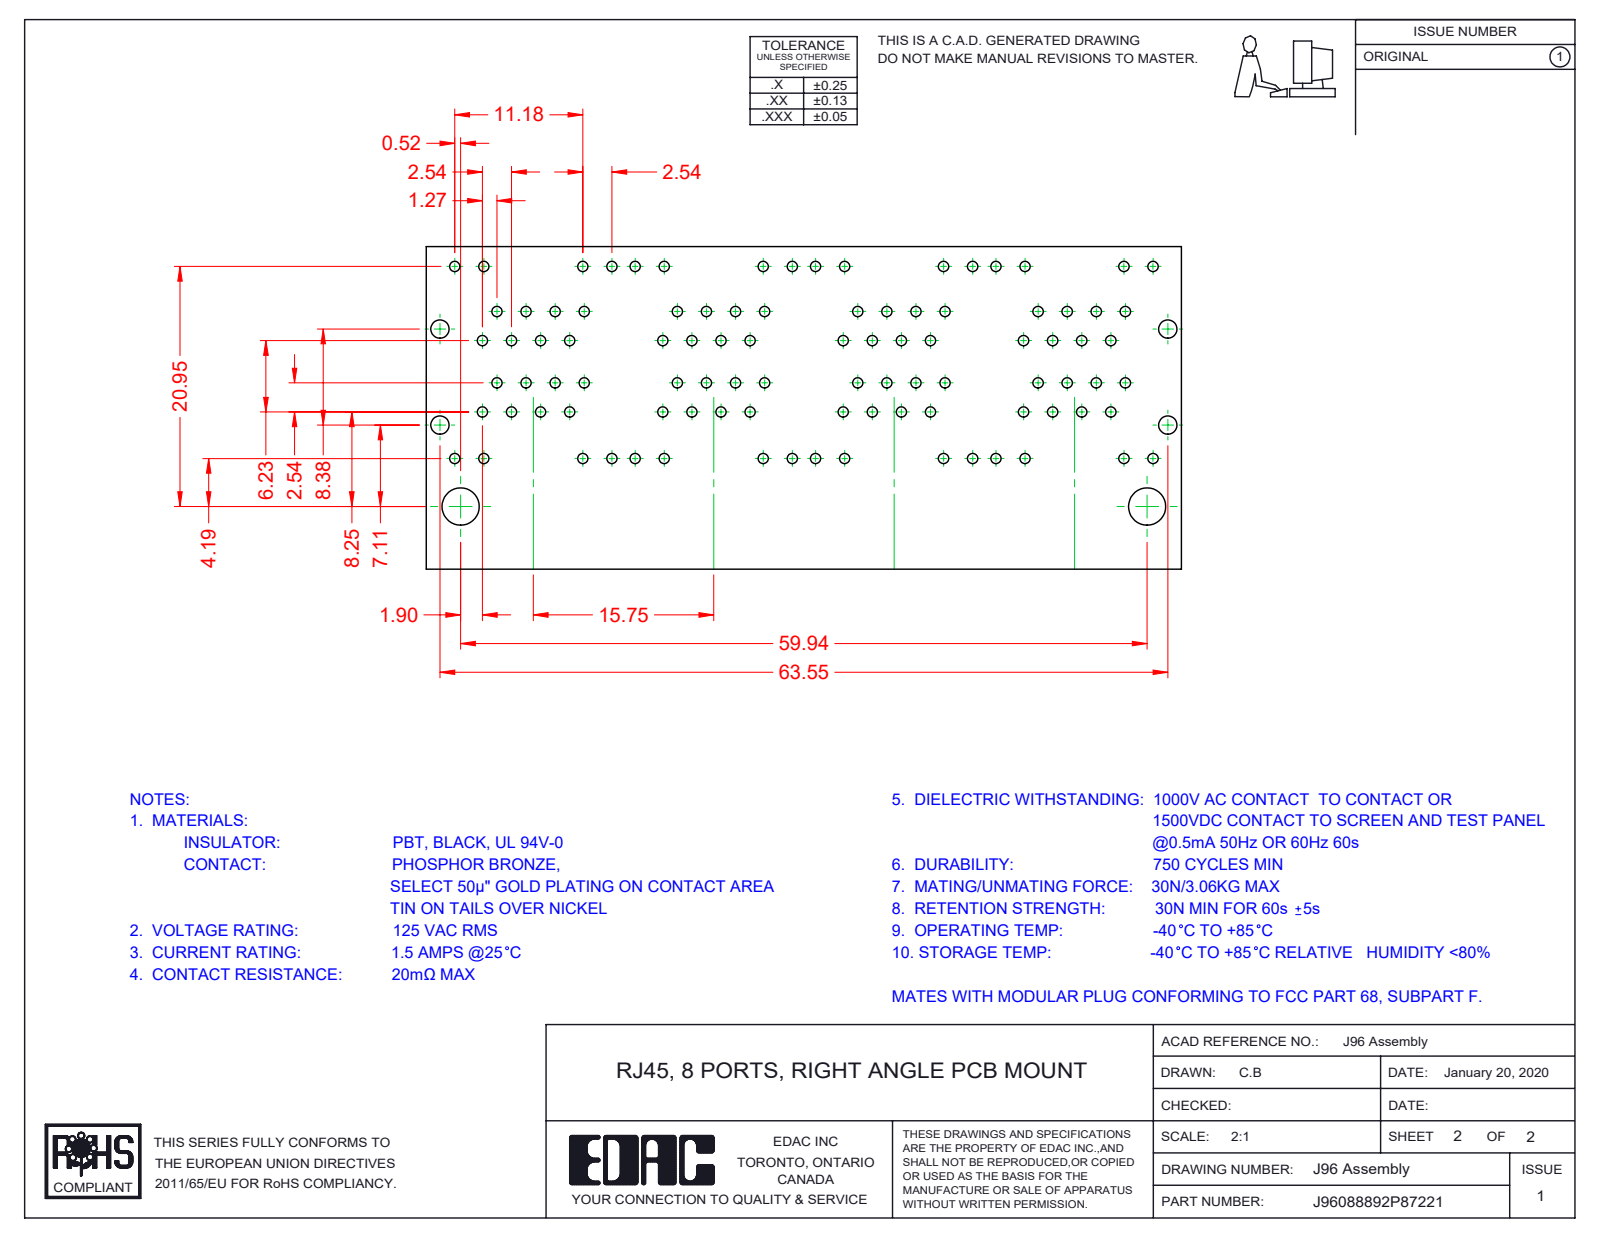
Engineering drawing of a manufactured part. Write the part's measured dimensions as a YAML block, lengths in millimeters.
part_name: "96 Contacts Upper; 96 Grounding_8 Ports; 96 LED LH Lower_8-Red-Yellow; J96088892P87221 (+8 more)"
step_written_by: "SolidWorks 2016 (CONFIG_CONTROL_DESIGN)"
units: millimeters
bodies: {solids: 96, faces: 7836, planar: 6105, cylindrical: 1420, other: 311}
overall_size: [67.35, 31.38, 28.68]
volume: 24149
surface_area: 63596
round_holes:
  - {diameter: 1.7, count: 3}
round_bosses_or_shafts:
  - {diameter: 1.68, count: 3}
partial_cylinders:
  - {radius: 0.25, count: 124}
  - {radius: 0.35, count: 73}
  - {radius: 1, count: 72}
  - {radius: 0.5, count: 49}
  - {radius: 0.91, count: 32}
  - {radius: 0.2, count: 27}
  - {radius: 0.27, count: 14}
  - {radius: 0.7, count: 11}
face_to_face_distances: [15.75, 0.35, 9.95, 1.17, 1.6, 0.54, 9.98, 10.18, 12.67, 3.37]
hole_center_spacings: [15.75, 31.5]
